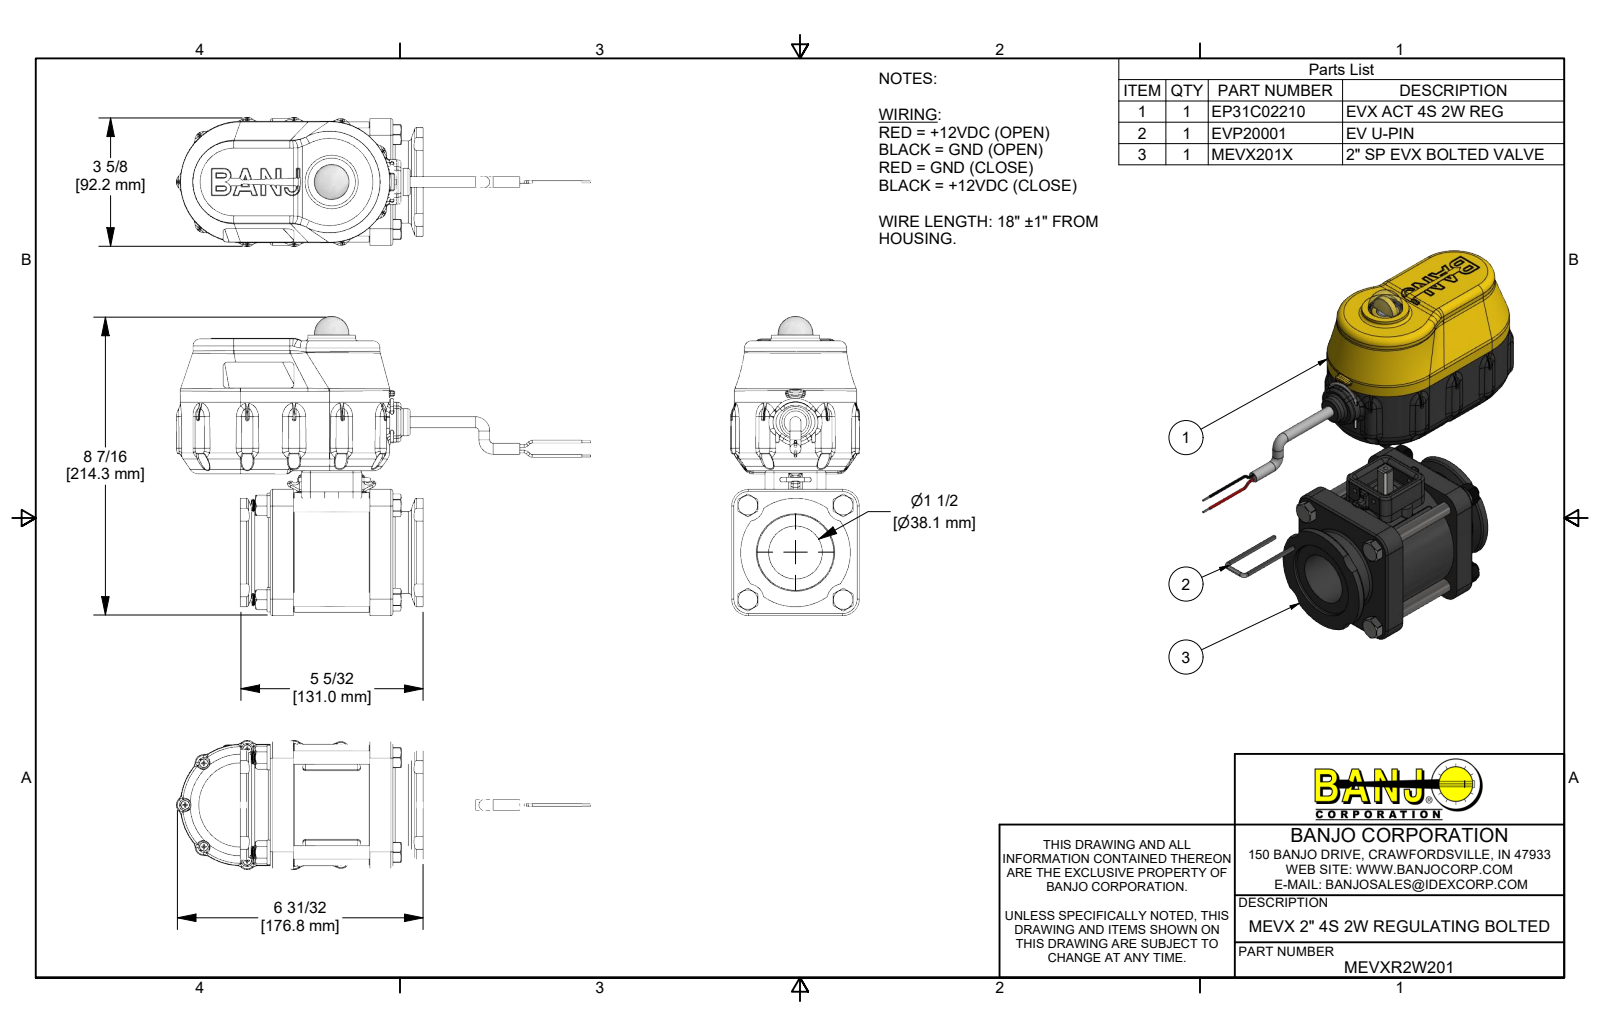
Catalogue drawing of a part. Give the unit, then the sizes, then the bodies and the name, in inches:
Units: inches
Overall size (bounding box): 11.685 × 8.437 × 3.63
Round holes (diameter × count): ⌀0.15 ×13, ⌀0.095 ×11, ⌀0.107 ×4, ⌀0.126 ×4, ⌀0.136 ×4, ⌀0.17 ×4, ⌀0.307 ×4, ⌀0.385 ×4, ⌀0.406 ×4, ⌀0.135 ×3, ⌀0.089 ×2, ⌀0.105 ×2
Round bosses / shafts (diameter × count): ⌀0.324 ×60, ⌀0.25 ×17, ⌀0.14 ×11, ⌀0.108 ×11, ⌀0.085 ×11, ⌀0.08 ×10, ⌀0.375 ×5, ⌀0.687 ×4
Partial cylindrical surfaces — rounded edges, fillets, slot ends (radius × count): R0.04 ×147, R0.02 ×91, R0.01 ×56, R0.005 ×43, R0.06 ×40, R0.08 ×28, R0.03 ×24, R0.015 ×22
Main face-to-face distances: 0.1, 2.565, 0.65, 2.808, 0.825, 2.633, 0.175, 1.983, 1.5, 0.85
Hole centre spacings: 1.283, 1.88, 2.659, 1.662, 2.088, 2.73, 2.967, 3.45
Volume: 64.83 in³ · Surface area: 643.9 in²
Bodies: 95 solids, 12311 faces (3476 planar, 3297 cylindrical, 5538 other)
Part name (STEP PRODUCT): MEVXR2W201; EP31C02210; 91400A119; 95584A200 (+8 more)
STEP written by: Autodesk Inventor 2019 (AUTOMOTIVE_DESIGN)
